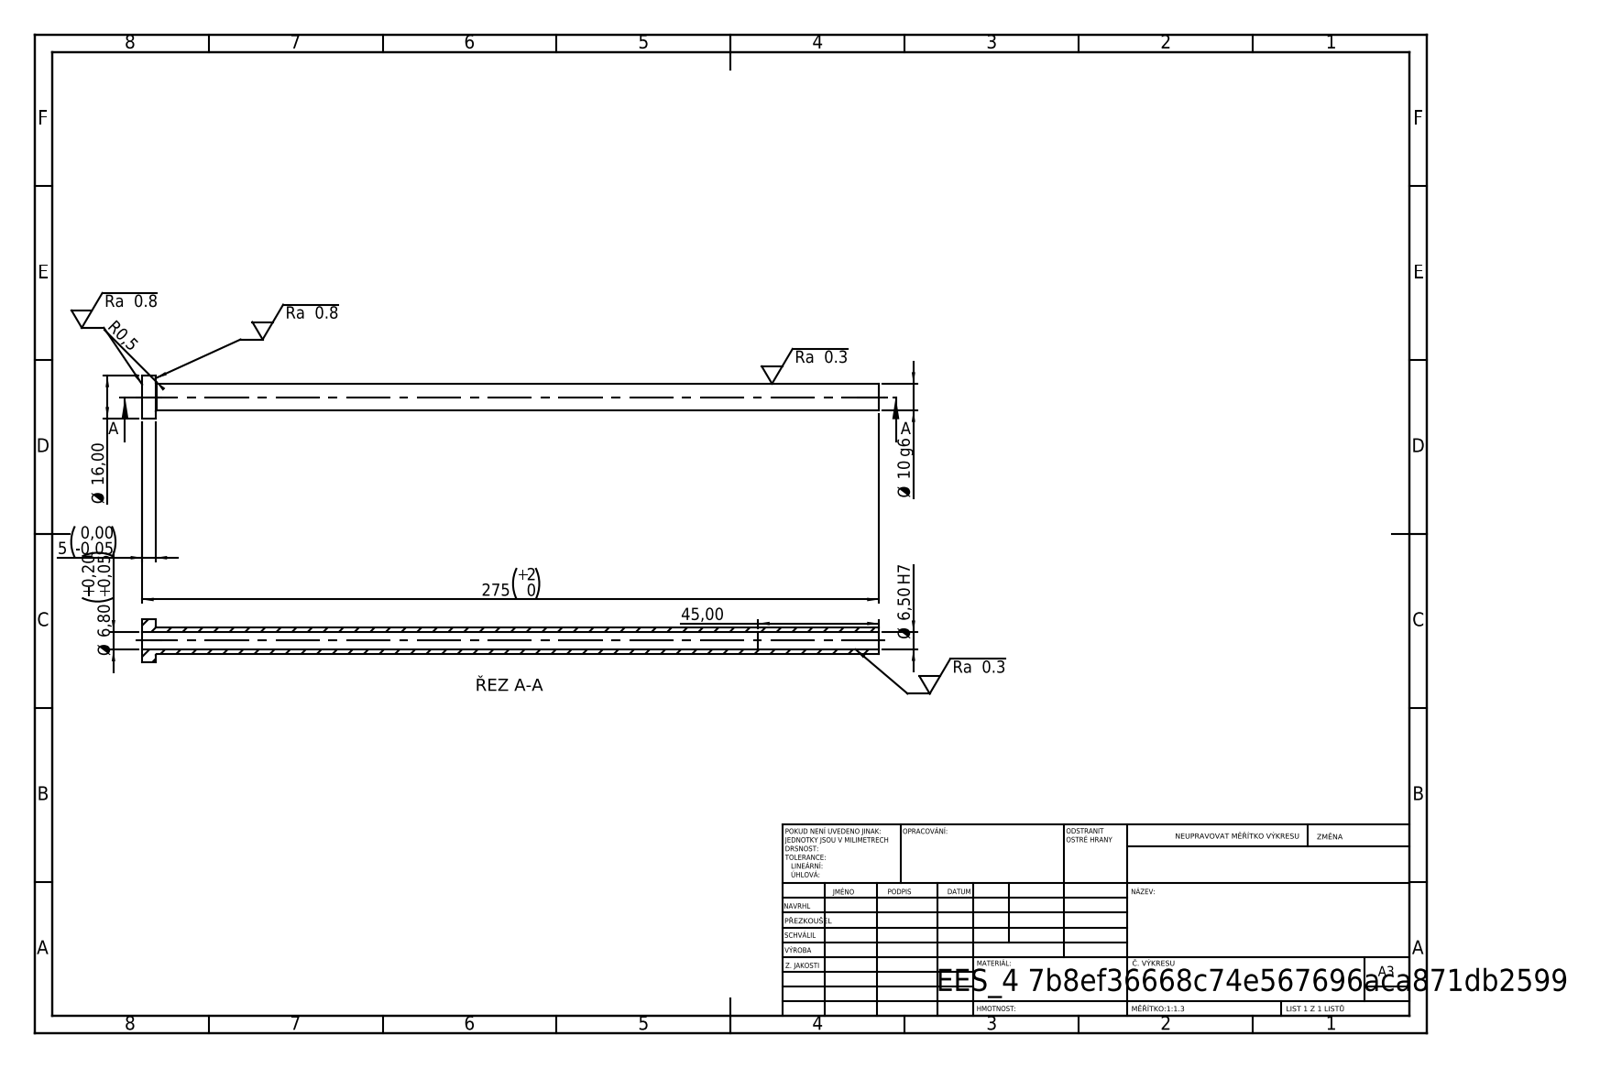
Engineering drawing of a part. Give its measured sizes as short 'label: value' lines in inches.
written by: SolidWorks 2019 (CONFIG_CONTROL_DESIGN)
unit: in
bodies: 1 solid, 14 faces (4 planar, 8 cylindrical, 2 other)
size: 10.827 × 0.63 × 0.63
volume: 0.755 in³; area: 23.09 in²
holes: 1× ⌀0.256, 1× ⌀0.268
bosses: 1× ⌀0.63, 1× ⌀0.394
face distances: 0.197, 10.827, 10.63, 9.055, 8.858, 1.772
